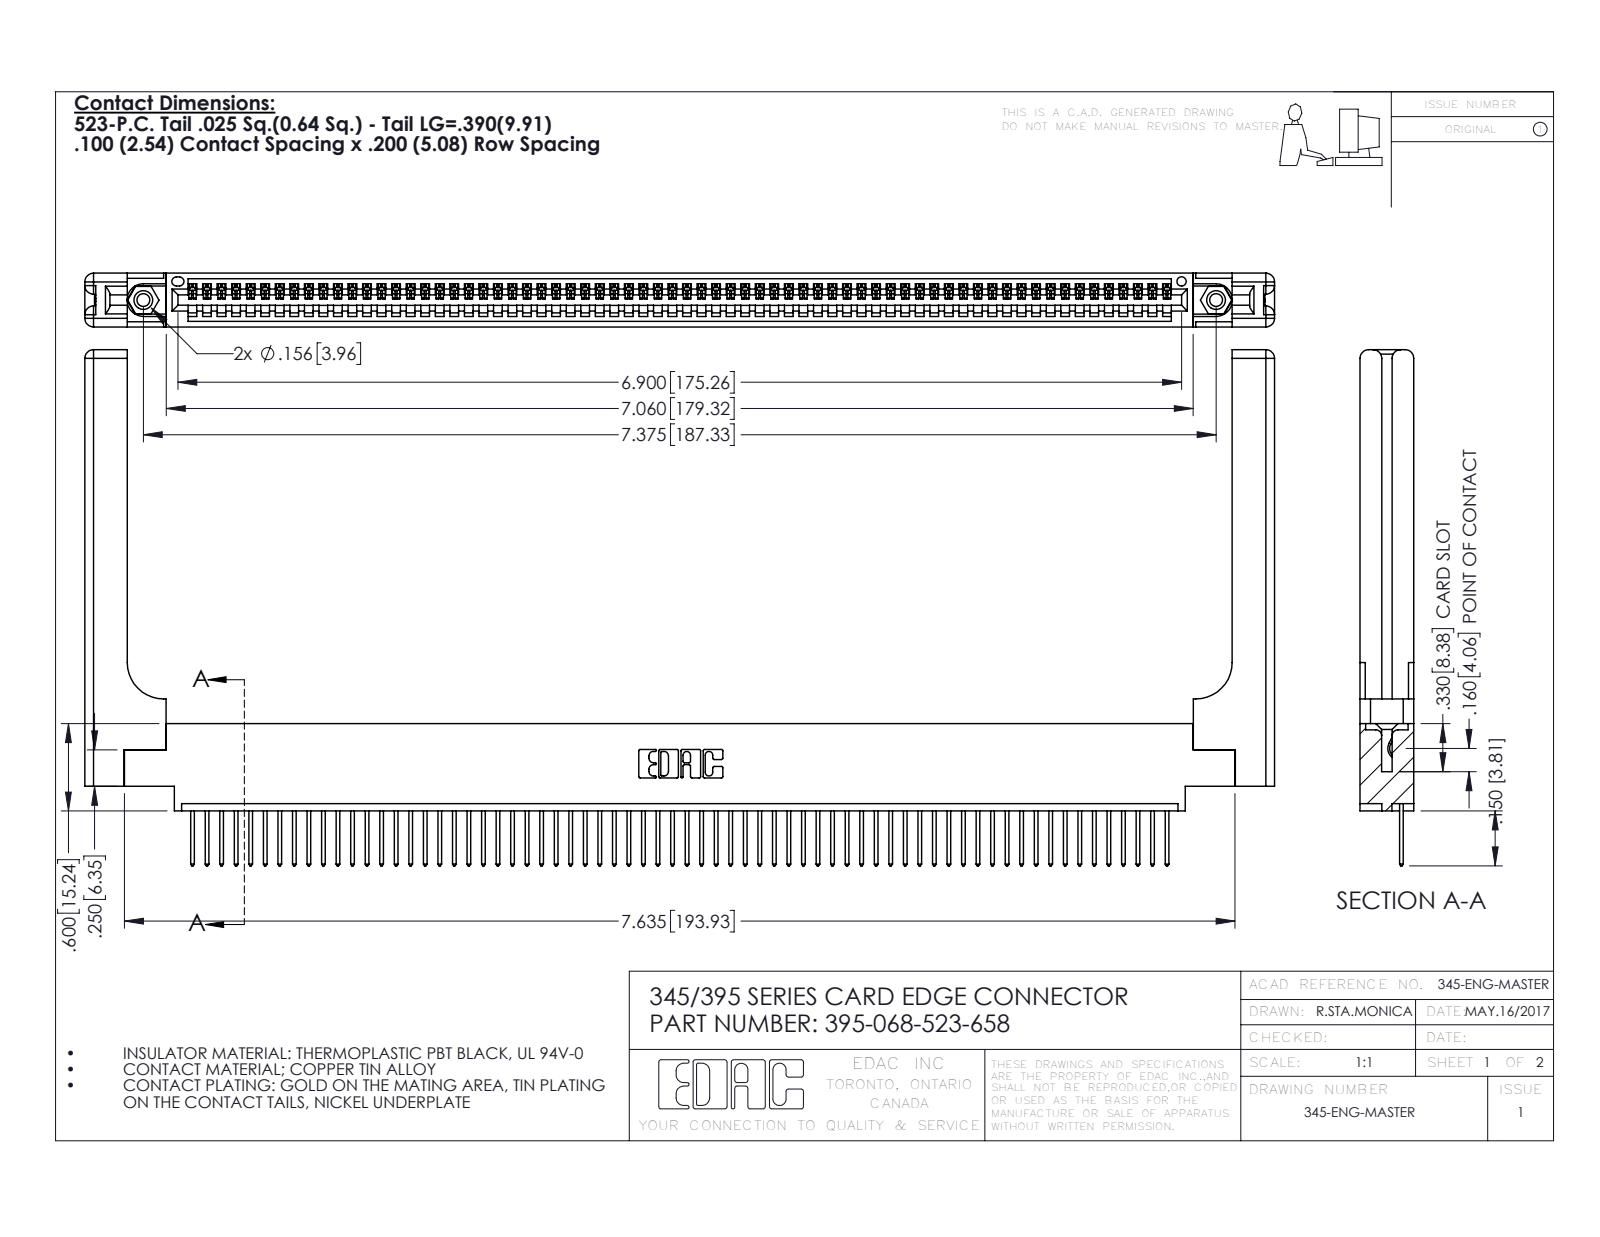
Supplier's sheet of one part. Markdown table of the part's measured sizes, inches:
| quantity | value |
| --- | --- |
| part name | 345 Part_0.170 Offset - 0.156 Dia-TH; 345-220-058_345-220-058; 395-068-523-658; 345-250-001_345-250-001-102 (+1 more) |
| STEP written by | SolidWorks 2016 (CONFIG_CONTROL_DESIGN) |
| units | inches |
| bodies | 73 solids, 4330 faces (2952 planar, 1318 cylindrical, 60 other) |
| overall size | 8.179 × 3.547 × 0.37 |
| volume | 1.728 in³ |
| surface area | 49.88 in² |
| round holes (diameter × count) | 0.089 × 2, 0.125 × 2, 0.156 × 2, 0.064 × 1 |
| round bosses / shafts (diameter × count) | 0.155 × 2 |
| partial cylindrical surfaces (radius × count) | 0.006 × 136, 0.01 × 136, 0.01 × 22, 0.06 × 16, 0.007 × 6, 0.031 × 6, 0.026 × 3, 0.03 × 2 |
| main face-to-face distances | 0.072, 0.298, 0.37, 0.098, 0.272, 0.025, 0.2, 0.225, 0.148, 0.15 |
| hole center spacings | 0.27, 7.139, 7.375 |
